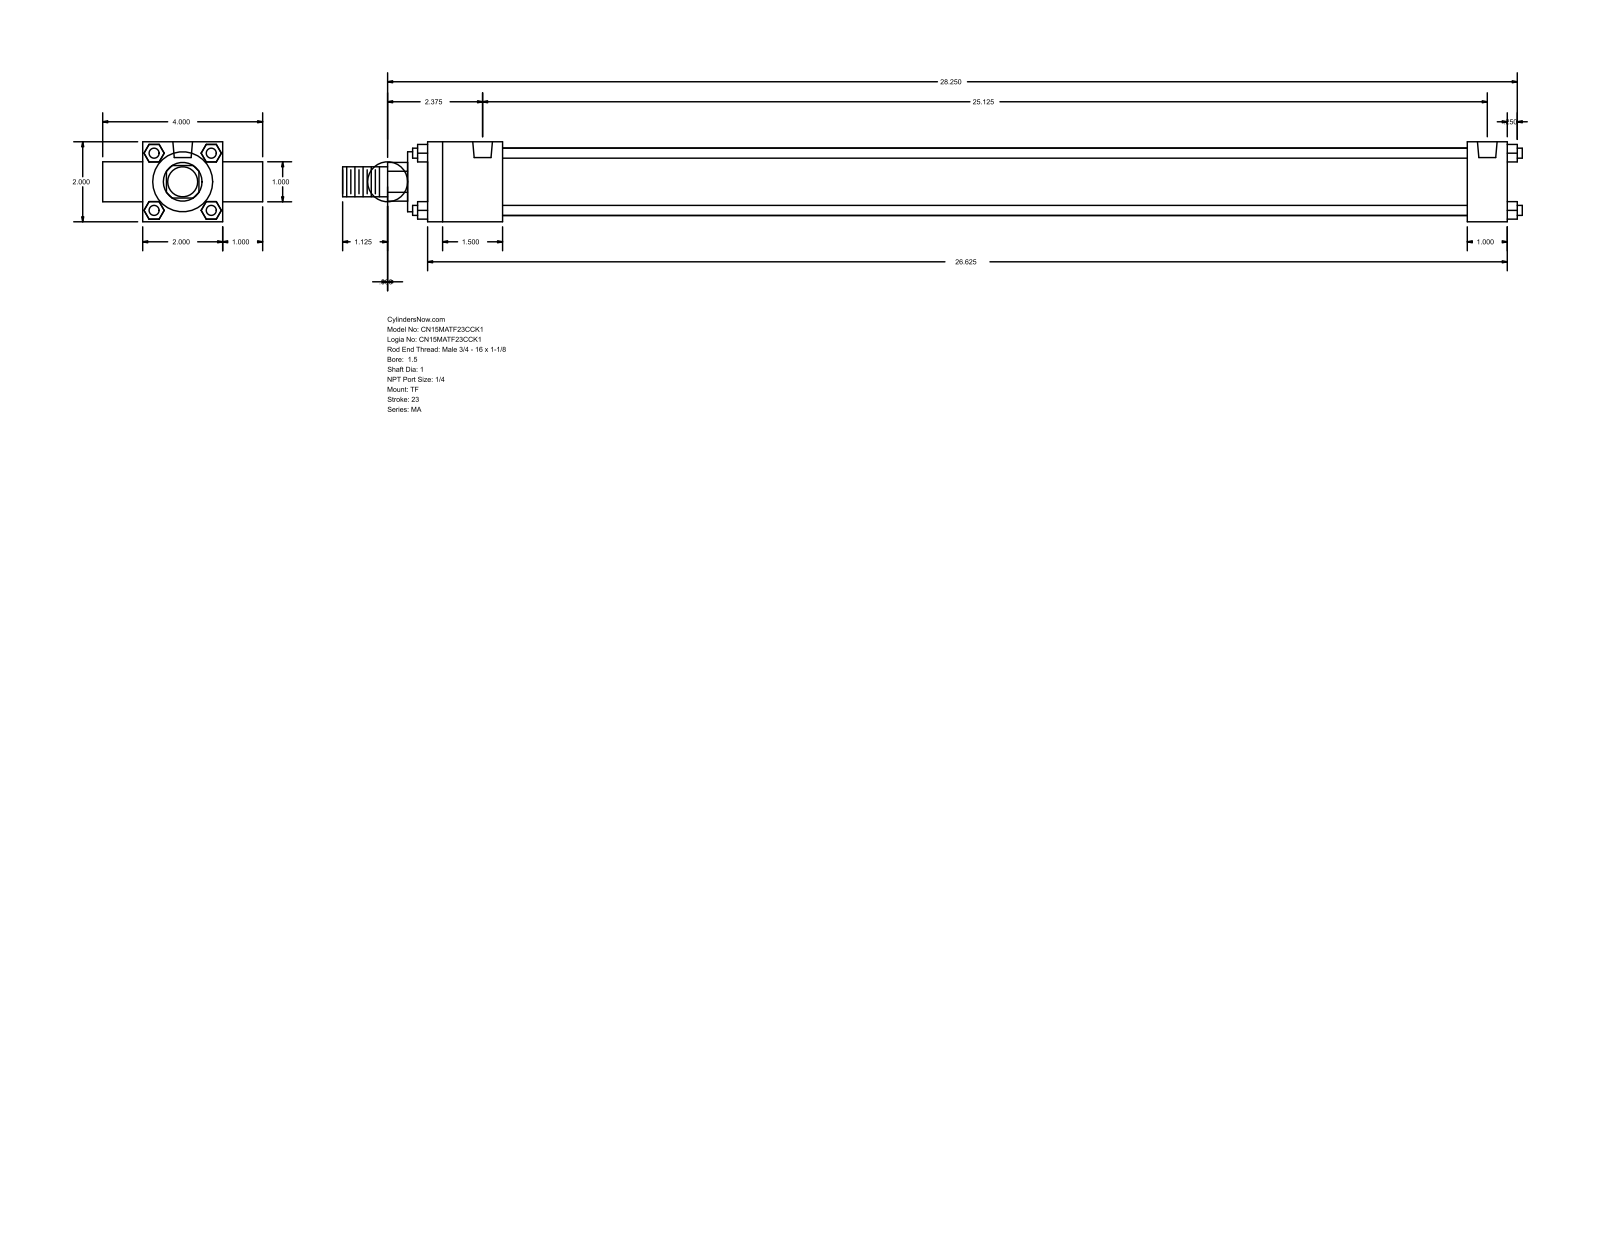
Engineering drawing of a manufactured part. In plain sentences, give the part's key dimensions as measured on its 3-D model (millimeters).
The part is named "MA_TF__0150_1". Its 3-D file was written by "GSSL Pune (CONFIG_CONTROL_DESIGN)". It is 0 solids with 120 faces: 92 planar, 28 cylindrical and 0 other. Overall it measures 749.3 by 101.6 by 50.8 millimeters. Round holes: 3 of diameter 7.94, 2 of diameter 12.49. Round bosses or shafts: 4 of diameter 6.35, 2 of diameter 25.4, 1 of diameter 42.93, 1 of diameter 38.1, 1 of diameter 19.05. Partial cylindrical surfaces (rounded edges, fillets, slot ends): 1 of radius 12.29. The main face-to-face distances are 50.8, 25.4, 685.8, 76.2, 6.35, 47.63, 660.4, 612.77, 638.17, 698.5. The hole center spacings are 638.17.
